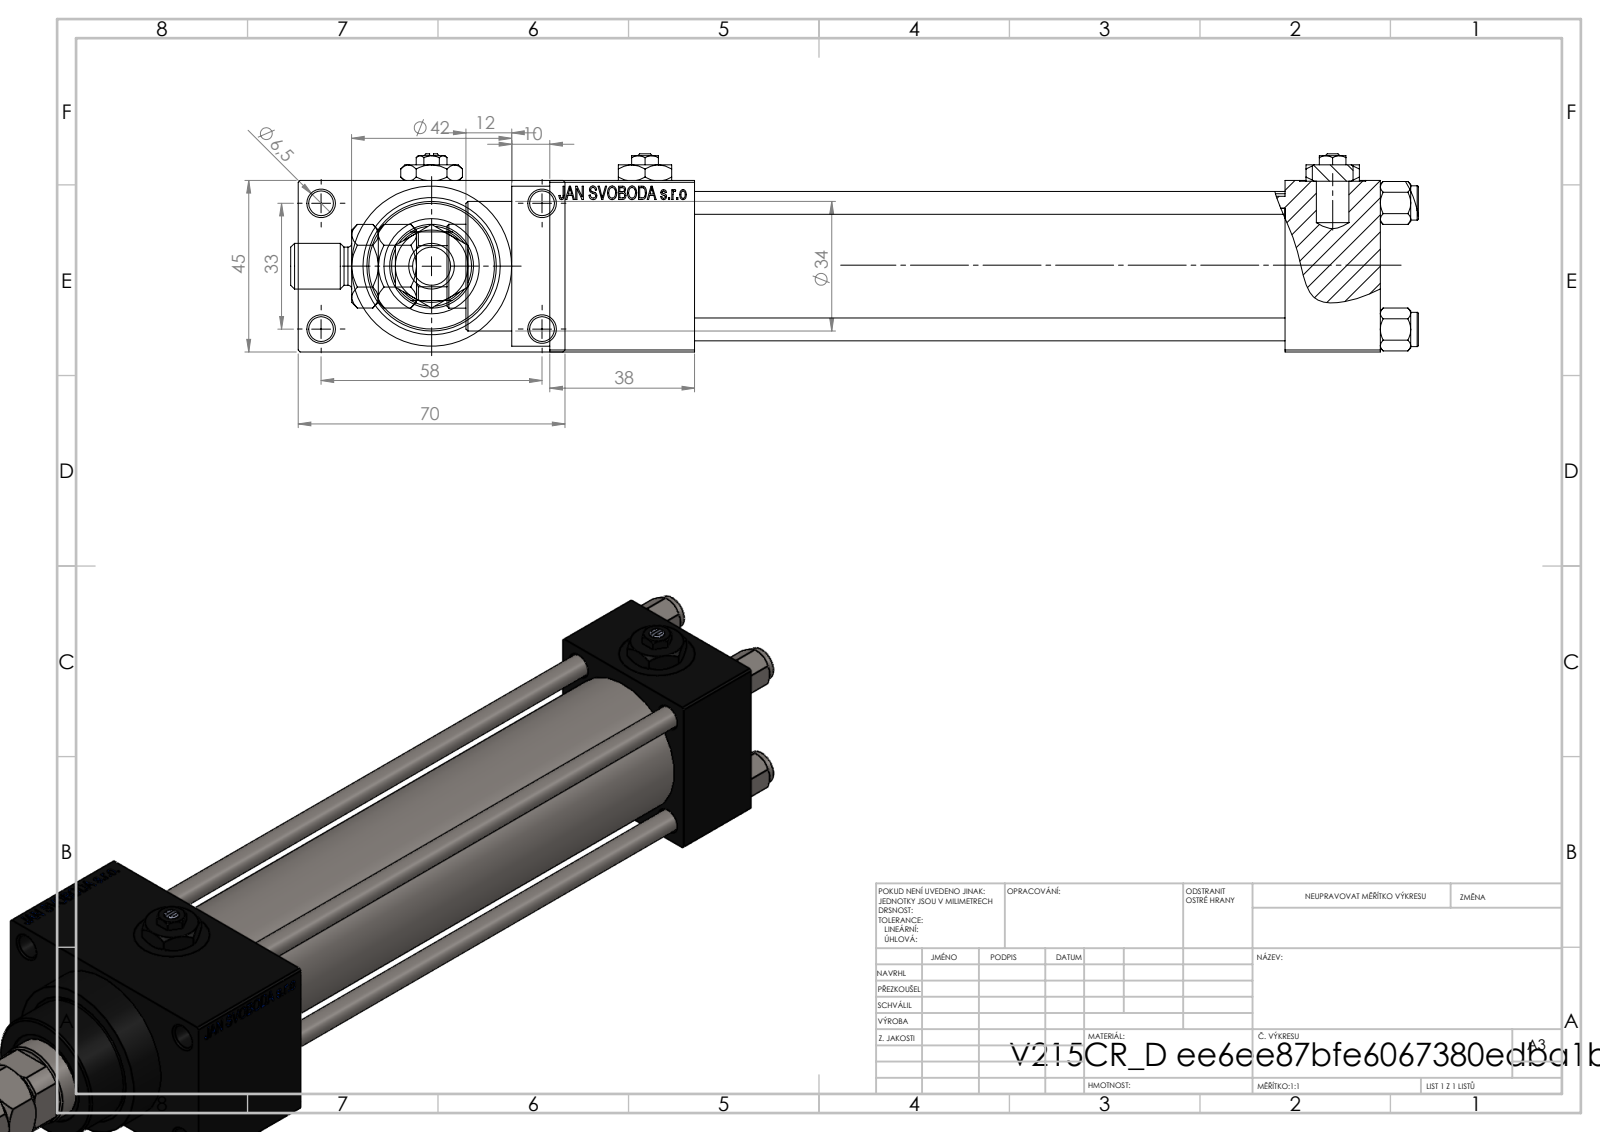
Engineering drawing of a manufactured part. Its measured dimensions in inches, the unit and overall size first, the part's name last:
Units: inches
Overall size (bounding box): 11.654 × 2.756 × 2.047
Round holes (diameter × count): ⌀0.236 ×4, ⌀0.256 ×4, ⌀0.518 ×4, ⌀0.787 ×4, ⌀0.276 ×3, ⌀0.413 ×1, ⌀0.866 ×1, ⌀0.945 ×1, ⌀0.984 ×1, ⌀1.26 ×1, ⌀1.299 ×1
Round bosses / shafts (diameter × count): ⌀0.354 ×4, ⌀1.654 ×1, ⌀1.496 ×1, ⌀1.339 ×1, ⌀0.472 ×1, ⌀0.394 ×1
Partial cylindrical surfaces — rounded edges, fillets, slot ends (radius × count): R0.413 ×1
Main face-to-face distances: 1.772, 0.984, 0.492, 6.102, 7.087, 2.264, 7.598, 1.496, 8.583, 2.756
Hole centre spacings: 0.488, 0.924, 1.307, 1.314, 1.392, 1.795, 2.219, 1.299
Volume: 20.44 in³ · Surface area: 189.4 in²
Bodies: 14 solids, 1252 faces (557 planar, 103 cylindrical, 592 other)
Part name (STEP PRODUCT): V215CR_D_TYCINKA; V215_VC_A; NUT_M5_D; V215CR_VCP_D (+3 more)
STEP written by: SolidWorks 2019 (CONFIG_CONTROL_DESIGN)
